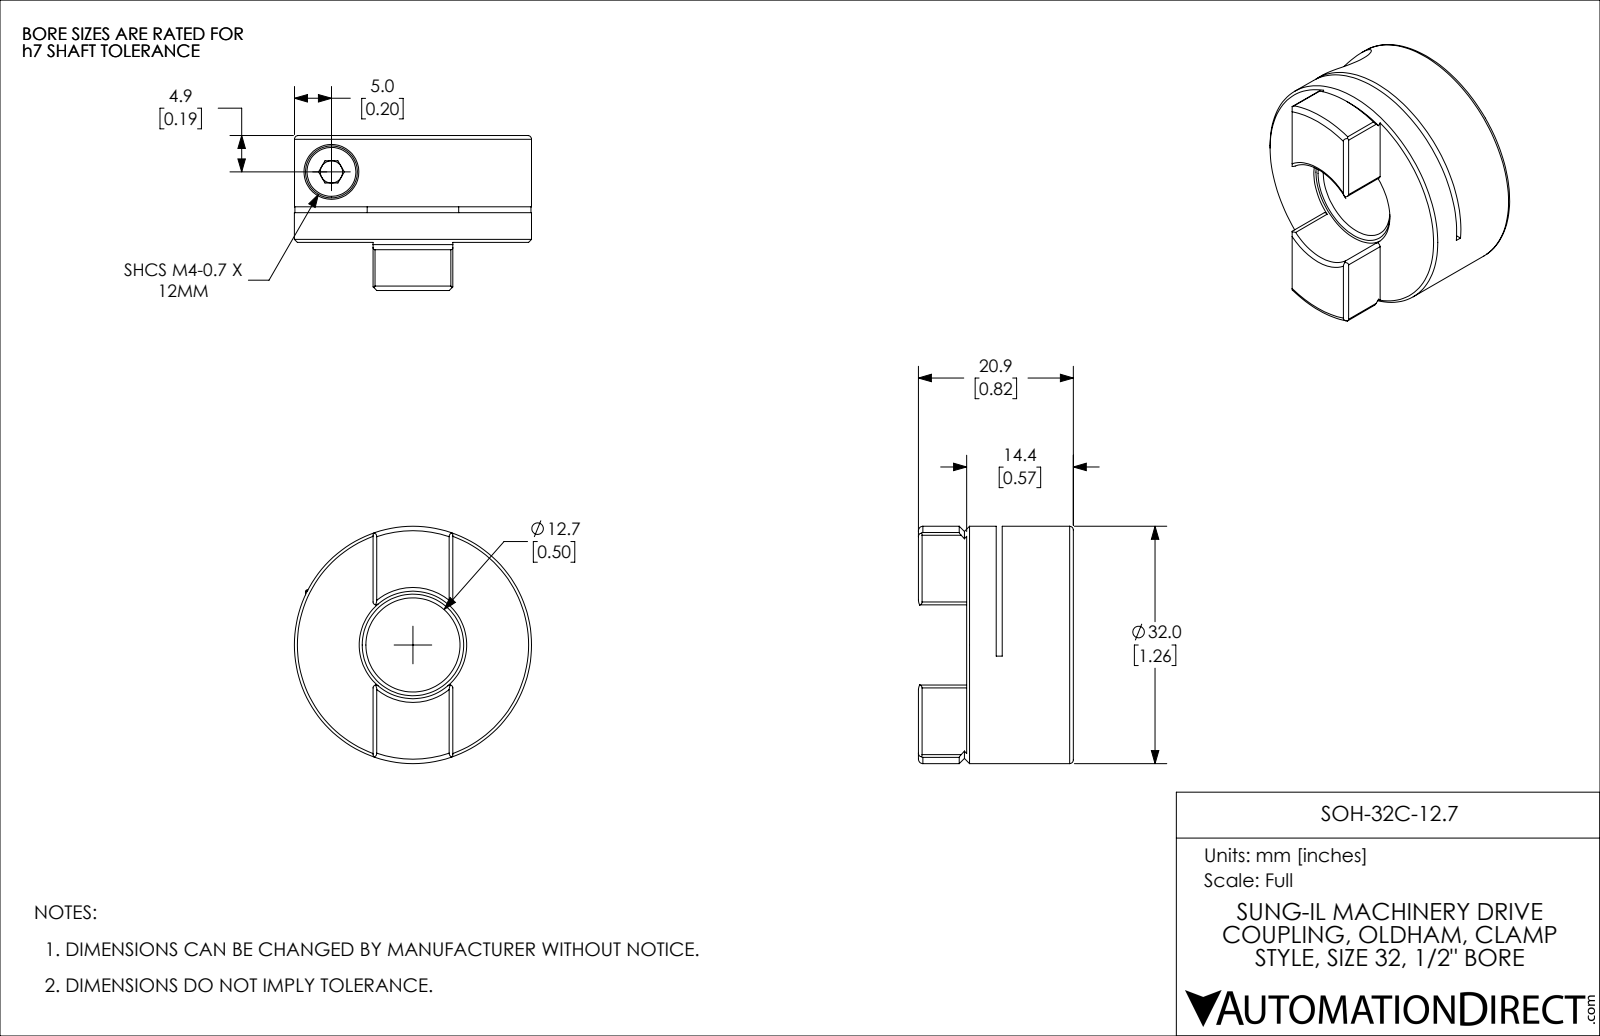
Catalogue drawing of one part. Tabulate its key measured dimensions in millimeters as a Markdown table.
| quantity | value |
| --- | --- |
| part name | SOH-32C-12 |
| STEP written by | SolidWorks 2021 (CONFIG_CONTROL_DESIGN) |
| units | millimeters |
| bodies | 2 solids, 97 faces (39 planar, 33 cylindrical, 25 other) |
| overall size | 32 × 32 × 20.9 |
| volume | 10 540 mm³ |
| surface area | 5 361 mm² |
| round holes (diameter × count) | 3 × 1, 3.3 × 1, 4.4 × 1, 7.4 × 1, 12 × 1, 14.5 × 1 |
| round bosses / shafts (diameter × count) | 32 × 1, 7 × 1, 4 × 1 |
| partial cylindrical surfaces (radius × count) | 0.4 × 8, 25 × 1 |
| main face-to-face distances | 14.4, 4, 10.4, 9.6, 0.8, 4.8, 20.9, 11.3, 10.5, 6.5 |
